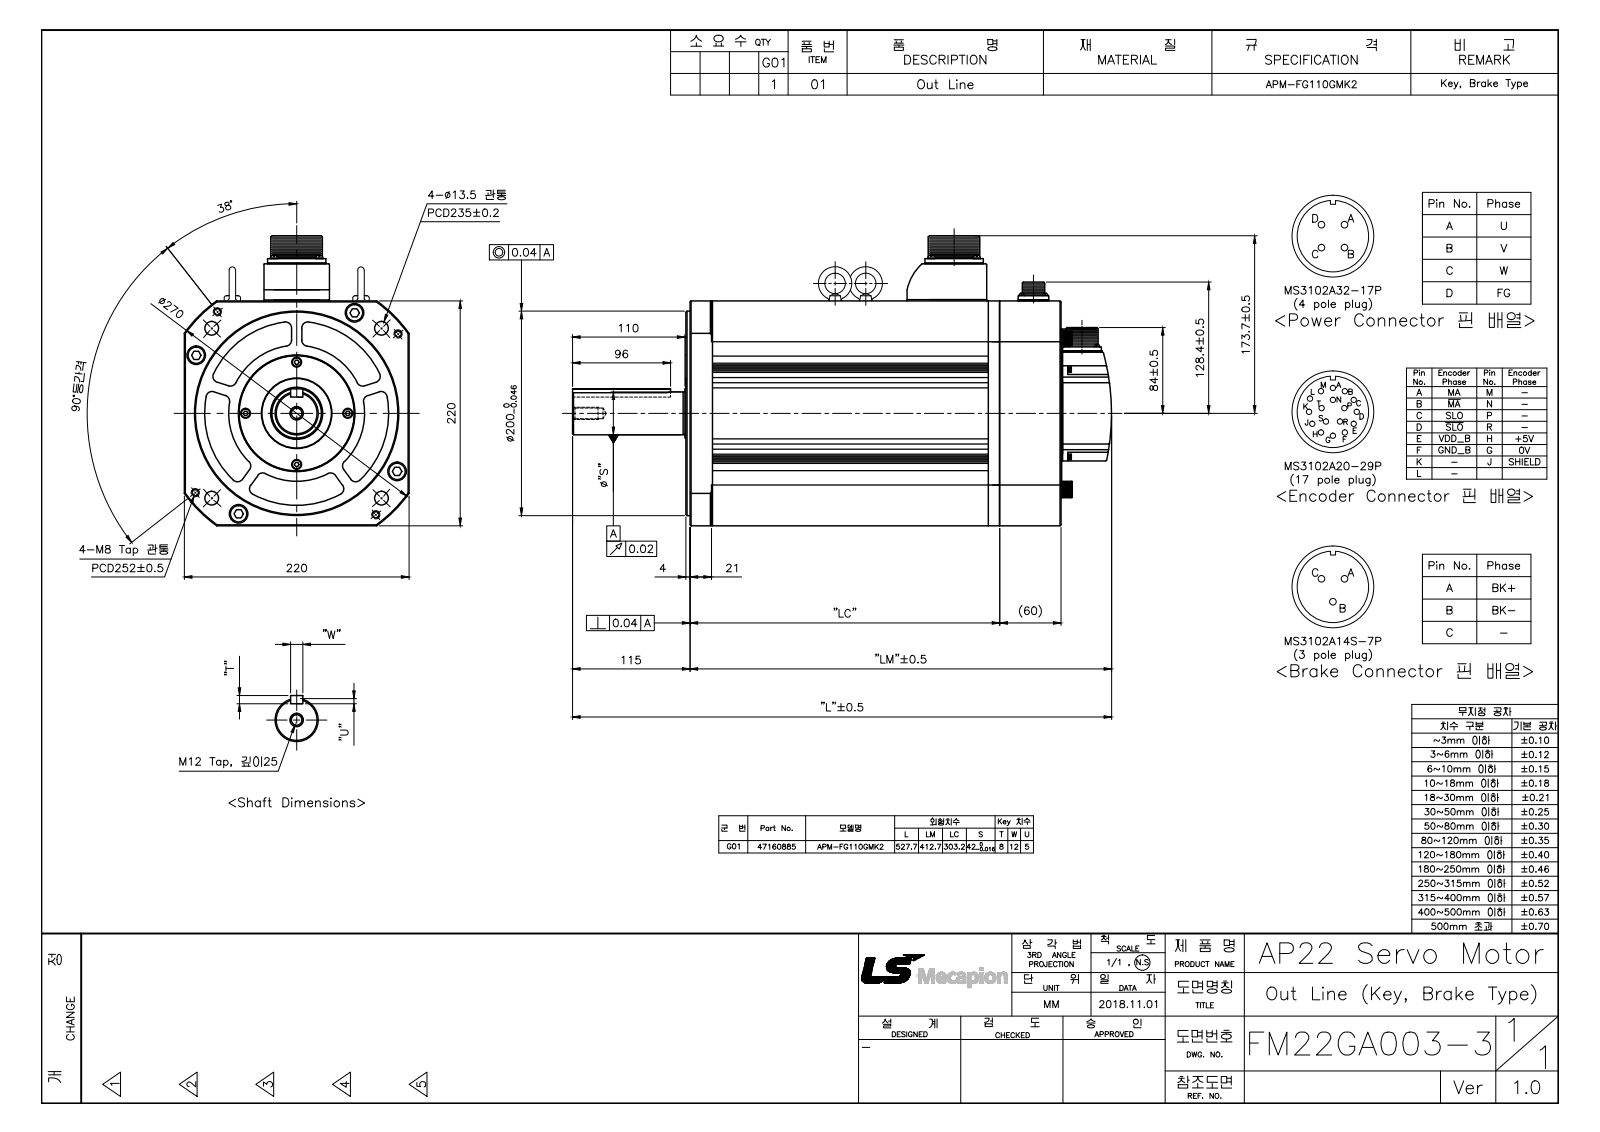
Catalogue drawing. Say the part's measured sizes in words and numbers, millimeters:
The part is named "FM22GA003-3_Out Line(APM-FG110G_K2)". Its 3-D file was written by "SolidWorks 2011 (AUTOMOTIVE_DESIGN)". It is 74 solids with 2570 faces: 898 planar, 1008 cylindrical and 664 other. Overall it measures 527.7 by 283.7 by 220 millimeters. Its volume is 15 890 000 cubic millimeters and its surface area 996 259 square millimeters. Round holes: 12 of diameter 2.5, 12 of diameter 3, 10 of diameter 3.05, 8 of diameter 8, 7 of diameter 11.2, 7 of diameter 17.5, 5 of diameter 18, 4 of diameter 3.3, 4 of diameter 3.5, 4 of diameter 3.6, 4 of diameter 3.7, 4 of diameter 4. Round bosses or shafts: 20 of diameter 1.6, 8 of diameter 5.4, 7 of diameter 16, 4 of diameter 8.5, 4 of diameter 7, 4 of diameter 6, 4 of diameter 5.5, 3 of diameter 10. Partial cylindrical surfaces (rounded edges, fillets, slot ends): 122 of radius 1, 25 of radius 6, 17 of radius 2, 16 of radius 5, 14 of radius 4, 12 of radius 4.5, 8 of radius 0.5, 4 of radius 2.5. The main face-to-face distances are 11.2, 281.2, 270, 40, 220, 180, 140, 21, 14, 60. The hole center spacings are 89.44, 156.9, 16.26, 17.11, 20.79, 23, 27.23, 29.4.
